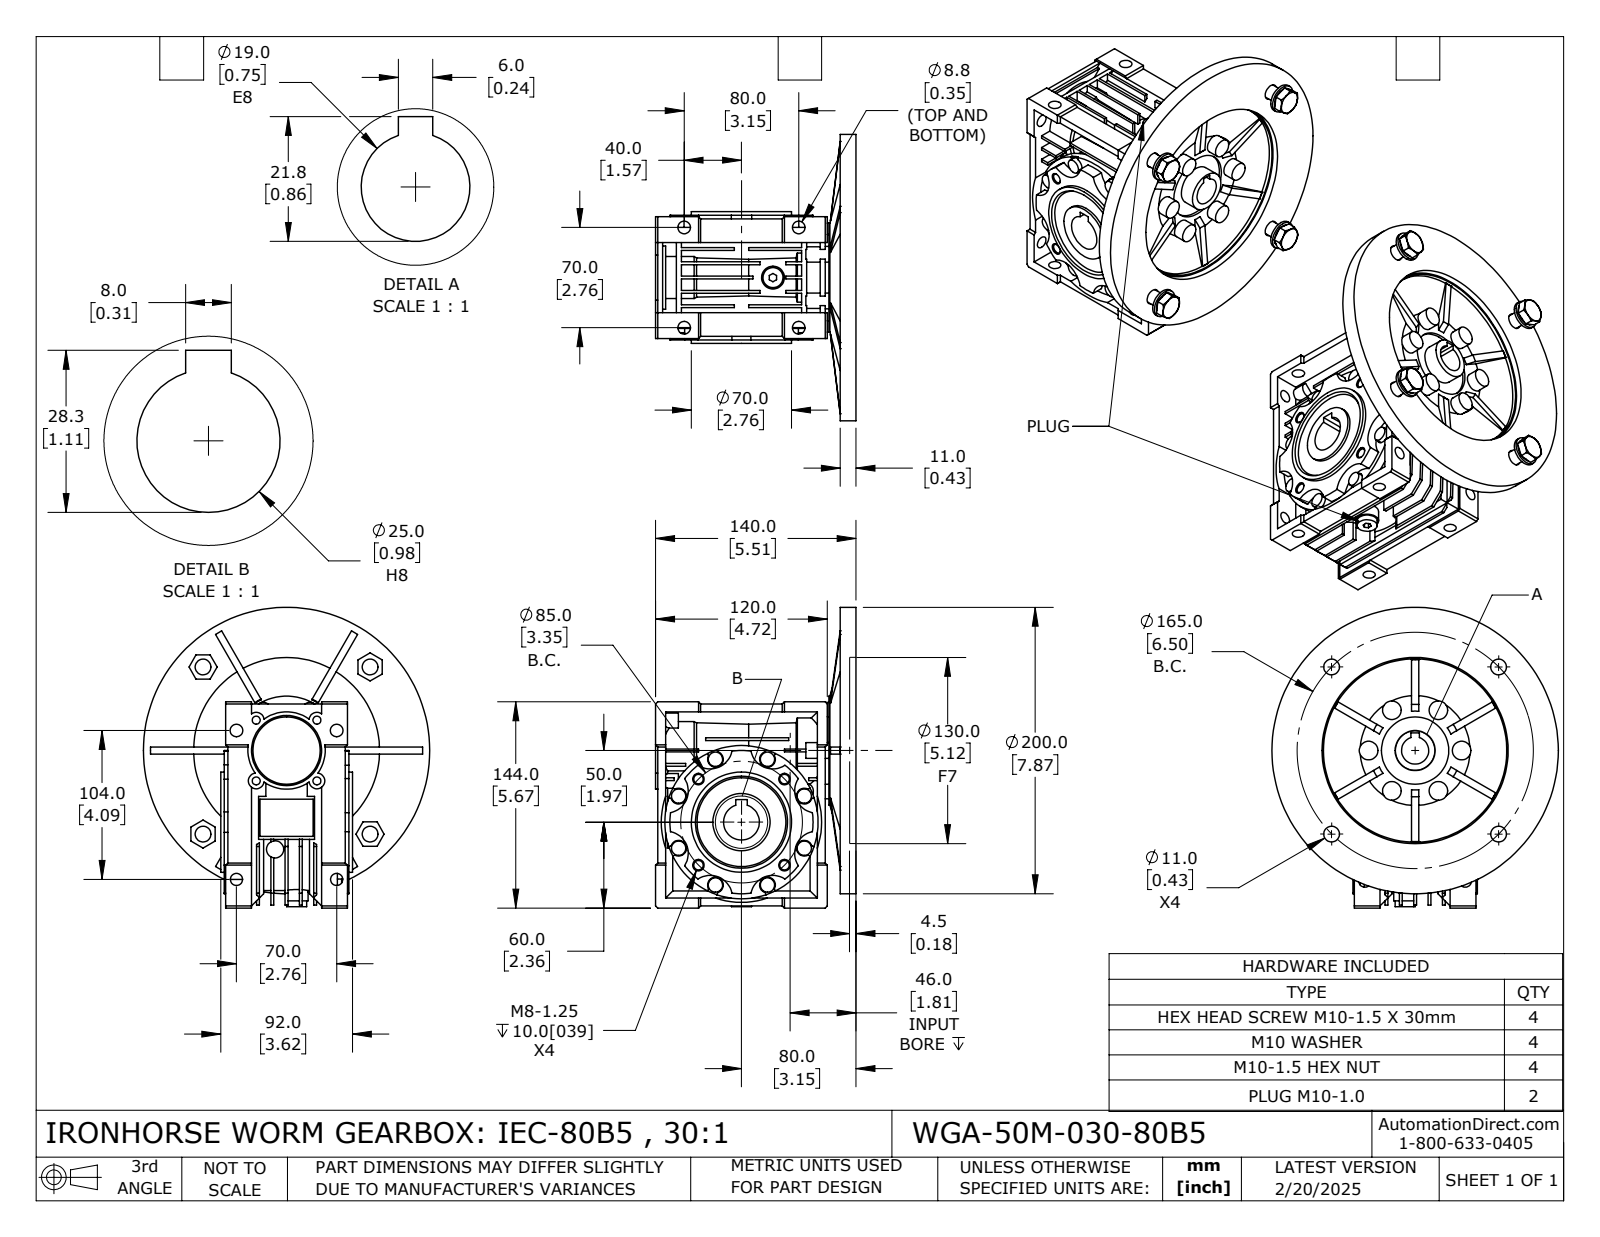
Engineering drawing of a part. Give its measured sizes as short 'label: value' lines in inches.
name: WGA-50M-030-80B5
written by: SolidWorks 2024 (CONFIG_CONTROL_DESIGN)
unit: in
bodies: 7 solids, 1029 faces (601 planar, 316 cylindrical, 112 other)
size: 8.268 × 7.874 × 5.512
volume: 76.4 in³; area: 442.4 in²
holes: 8× ⌀0.346, 6× ⌀0.335, 4× ⌀0.219, 4× ⌀0.433, 2× ⌀0.262, 2× ⌀0.262, 2× ⌀0.354, 1× ⌀0.748, 1× ⌀0.787, 1× ⌀0.984, 1× ⌀1.102, 1× ⌀1.339
bosses: 8× ⌀0.394, 6× ⌀0.512, 2× ⌀0.63, 2× ⌀0.551, 2× ⌀0.386, 2× ⌀0.327, 1× ⌀7.874, 1× ⌀4.213
rounds: 18× R0.217, 8× R0.236, 8× R0.591, 8× R0.61, 1× R0.817, 1× R1.811, 1× R1.878, 1× R1.969
face distances: 0.433, 0.315, 0.079, 0.394, 0.276, 0.059, 0.217, 0.787, 0.197, 2.165
hole spacings: 3.456, 2.756, 1.181, 1.67, 1.673, 2.067, 2.366, 3.248
